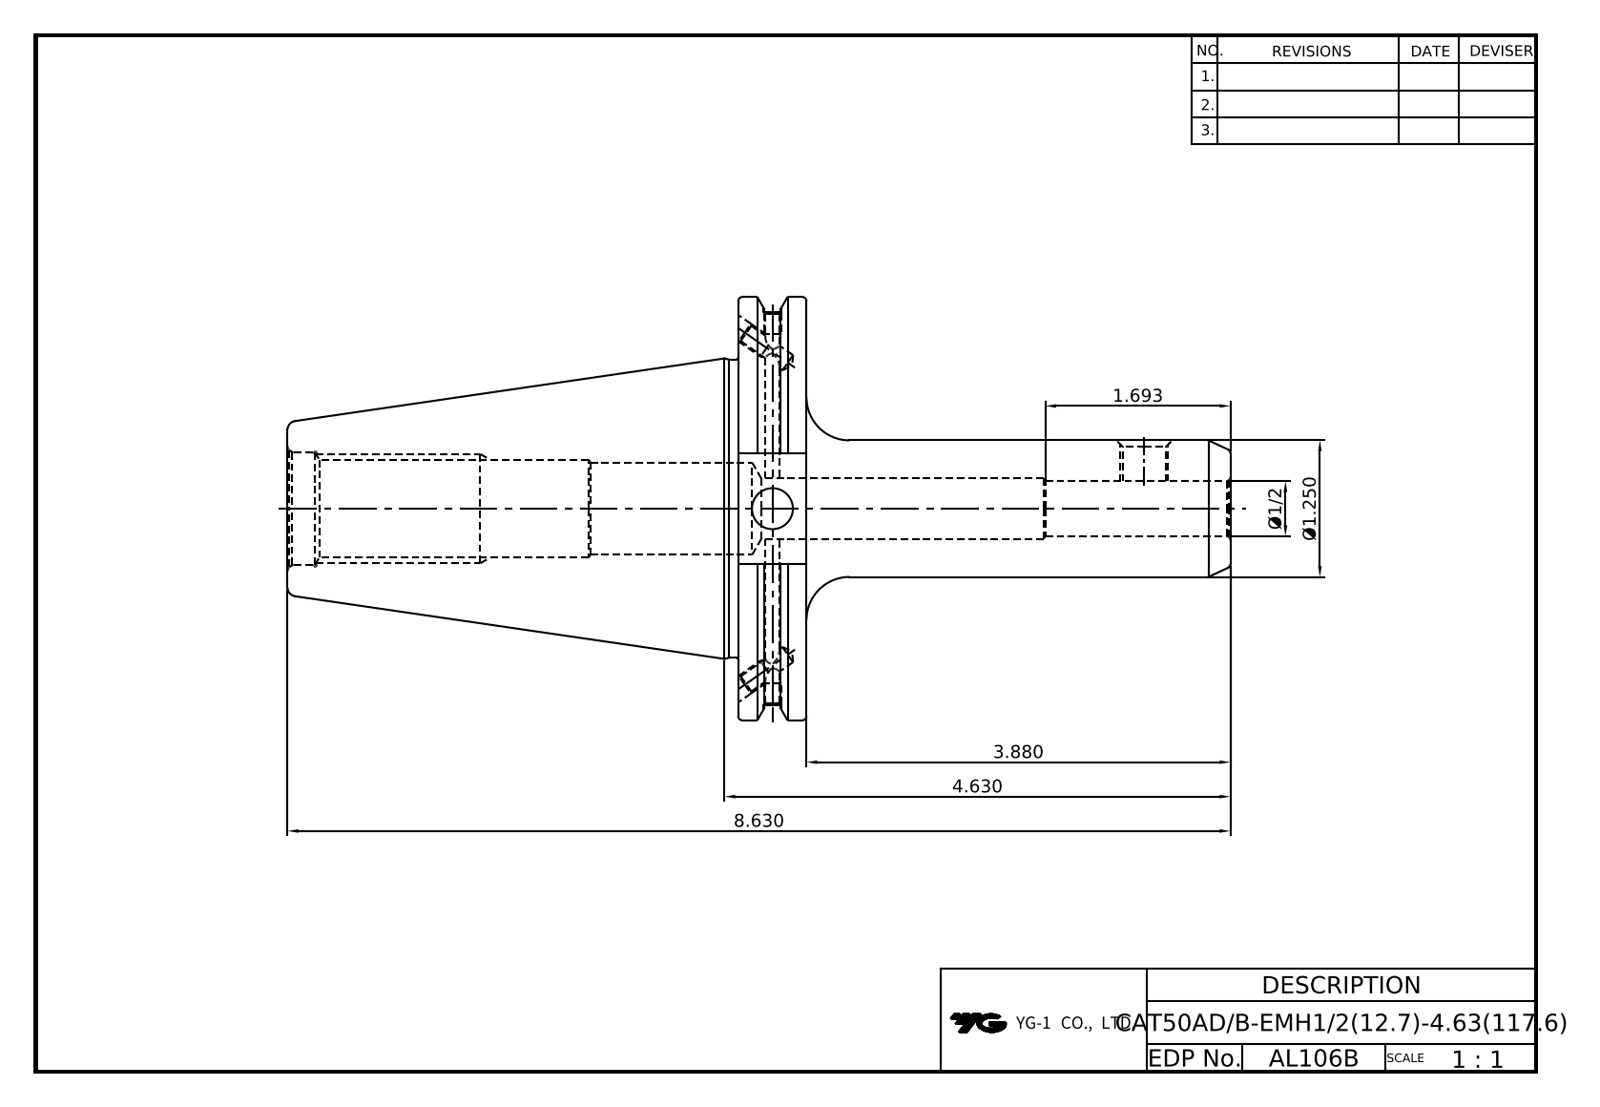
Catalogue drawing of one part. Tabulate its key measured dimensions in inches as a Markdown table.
| quantity | value |
| --- | --- |
| part name | LO-CAT50ADB-EMH12.7-117.6 |
| STEP written by | Autodesk Inventor 2024 (AUTOMOTIVE_DESIGN) |
| units | inches |
| bodies | 1 solid, 88 faces (36 planar, 27 cylindrical, 25 other) |
| overall size | 8.63 × 3.875 × 3.728 |
| volume | 23.51 in³ |
| surface area | 91.02 in² |
| round holes (diameter × count) | 0.128 × 2, 0.163 × 2, 0.165 × 2, 0.197 × 2, 0.375 × 1, 0.383 × 1, 0.5 × 1, 0.551 × 1, 0.846 × 1, 0.865 × 1, 1.031 × 1 |
| round bosses / shafts (diameter × count) | 3.875 × 1, 3.594 × 1, 2.726 × 1, 1.25 × 1 |
| main face-to-face distances | 0.625, 4.125, 4.75, 8.63, 4.505, 3.88, 2.875, 1.02, 4.363, 0.238 |
